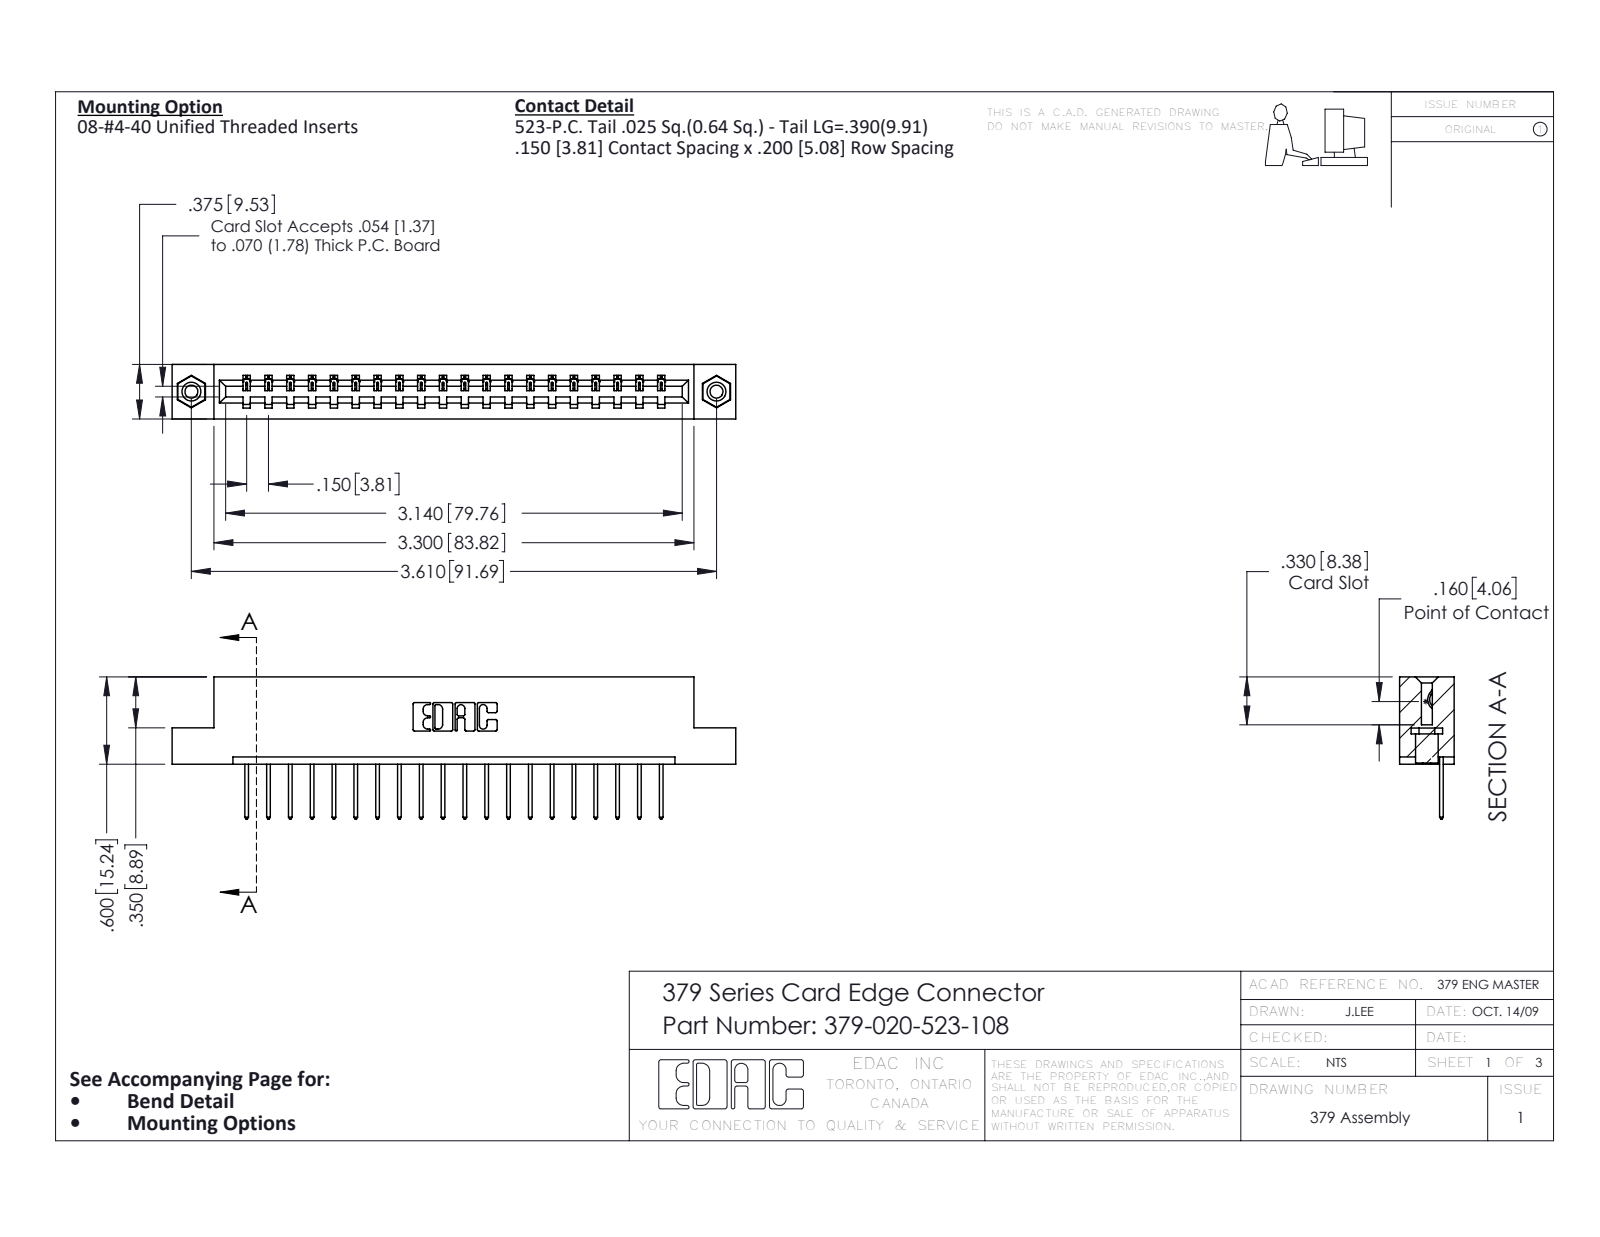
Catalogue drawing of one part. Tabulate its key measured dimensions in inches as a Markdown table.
| quantity | value |
| --- | --- |
| part name | 379 Part_Flush - .156 Dia - TI; 345-250-001_345-250-003-102; 345-292-001_345-293-123; 379-020-523-108 |
| STEP written by | SolidWorks 2016 (CONFIG_CONTROL_DESIGN) |
| units | inches |
| bodies | 23 solids, 1334 faces (942 planar, 376 cylindrical, 16 other) |
| overall size | 3.875 × 0.977 × 0.375 |
| volume | 0.614 in³ |
| surface area | 15.87 in² |
| round holes (diameter × count) | 0.089 × 2, 0.125 × 2, 0.156 × 2 |
| round bosses / shafts (diameter × count) | 0.155 × 2 |
| partial cylindrical surfaces (radius × count) | 0.006 × 40, 0.01 × 40, 0.01 × 22, 0.007 × 6, 0.031 × 6, 0.026 × 3, 0.014 × 1, 0.022 × 1 |
| main face-to-face distances | 0.3, 0.075, 0.375, 0.6, 0.225, 0.15, 0.2, 0.45, 0.275, 0.1 |
| hole center spacings | 3.61 |
